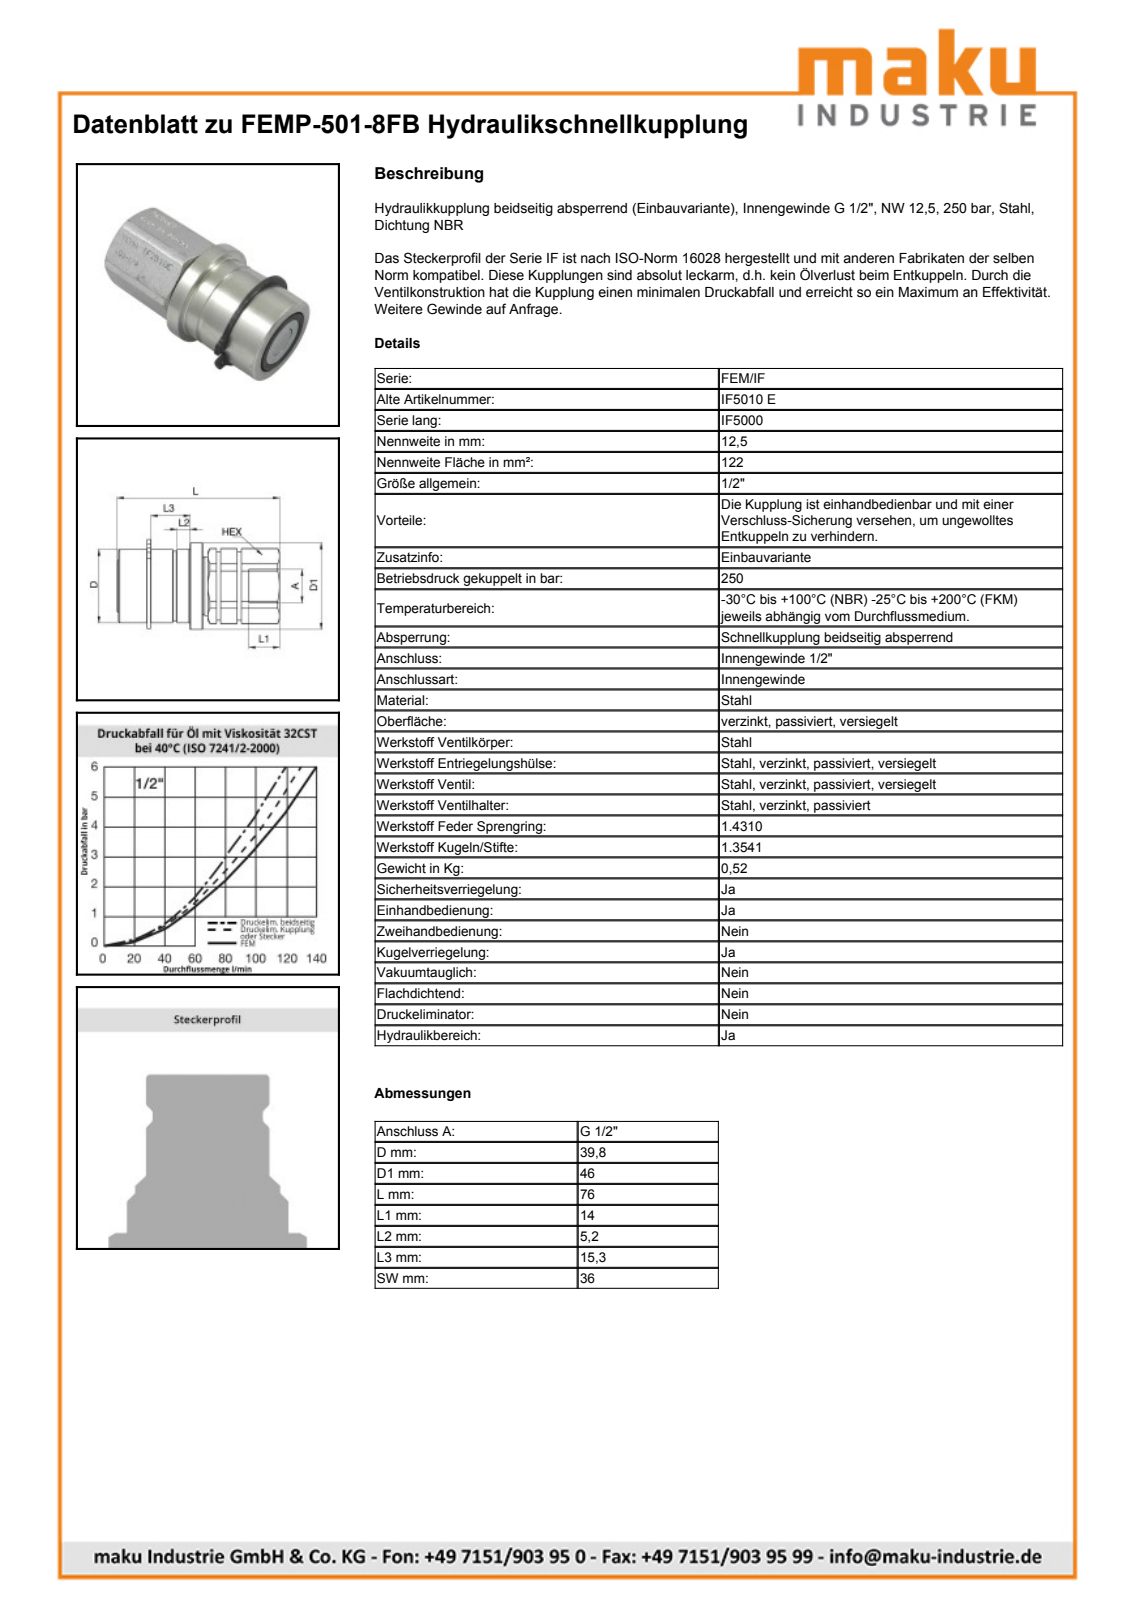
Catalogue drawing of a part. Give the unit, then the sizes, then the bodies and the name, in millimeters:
Units: millimetres
Overall size (bounding box): 75.9 × 47.17 × 46
Round holes (diameter × count): ⌀2.5 ×2, ⌀15.75 ×1, ⌀18.63 ×1, ⌀24.7 ×1, ⌀31.6 ×1, ⌀34.4 ×1, ⌀35.8 ×1
Round bosses / shafts (diameter × count): ⌀46 ×1, ⌀40 ×1, ⌀39.8 ×1, ⌀37.5 ×1, ⌀32.6 ×1, ⌀31.28 ×1, ⌀31.2 ×1, ⌀30 ×1
Partial cylindrical surfaces — rounded edges, fillets, slot ends (radius × count): R3 ×2, R7 ×2, R21.75 ×1, R24.23 ×1
Main face-to-face distances: 36, 63.8, 75.6, 11.8, 62.2, 1.6, 13.4, 74.9, 12.7, 11.1
Hole centre spacings: 20.78, 10
Volume: 85 878 mm³ · Surface area: 17 218 mm²
Bodies: 2 solids, 152 faces (33 planar, 59 cylindrical, 60 other)
Part name (STEP PRODUCT): FEMP-501-8FB
STEP written by: SolidWorks 2009 (AUTOMOTIVE_DESIGN)
